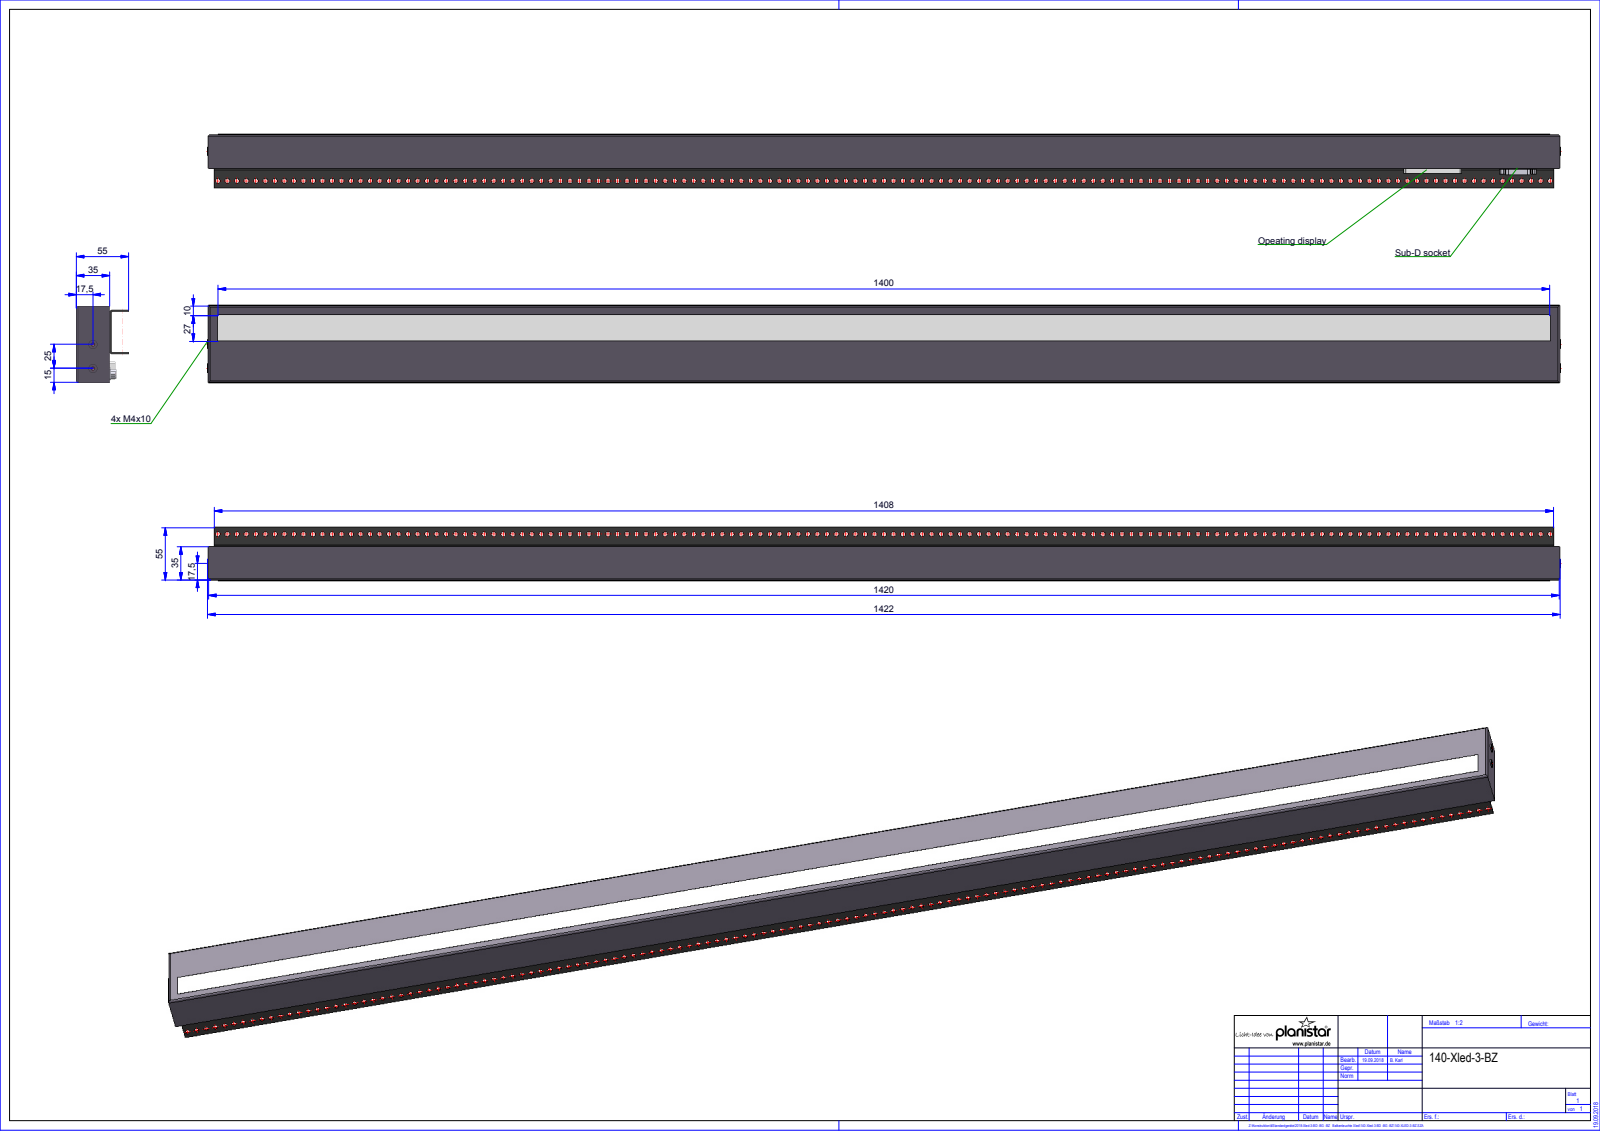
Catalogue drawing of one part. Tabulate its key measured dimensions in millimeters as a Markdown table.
| quantity | value |
| --- | --- |
| part name | Root; Baugruppe_Xled-2-VD; QUADER_0; Baugruppe_Baugruppe (+5 more) |
| STEP written by | HiCAD 2015 2002.1 Build 408 (AUTOMOTIVE_DESIGN) |
| units | millimeters |
| bodies | 13 solids, 443 faces (86 planar, 344 cylindrical, 13 other) |
| overall size | 1422 × 80 × 55.1 |
| volume | 4 202 000 mm³ |
| surface area | 567 173 mm² |
| round holes (diameter × count) | 5 × 141, 2.5 × 2, 3 × 2, 3.3 × 2, 4 × 2 |
| round bosses / shafts (diameter × count) | 1 × 5, 8 × 3, 9 × 2, 3.6 × 2 |
| partial cylindrical surfaces (radius × count) | 0.2 × 12, 2 × 10, 1.5 × 4, 2.1 × 4, 2.5 × 4, 1 × 2 |
| main face-to-face distances | 2, 35, 37, 80, 44, 35.1, 37.1, 4, 76, 30 |
| hole center spacings | 10, 20, 30, 40, 50, 60, 70, 80 |
